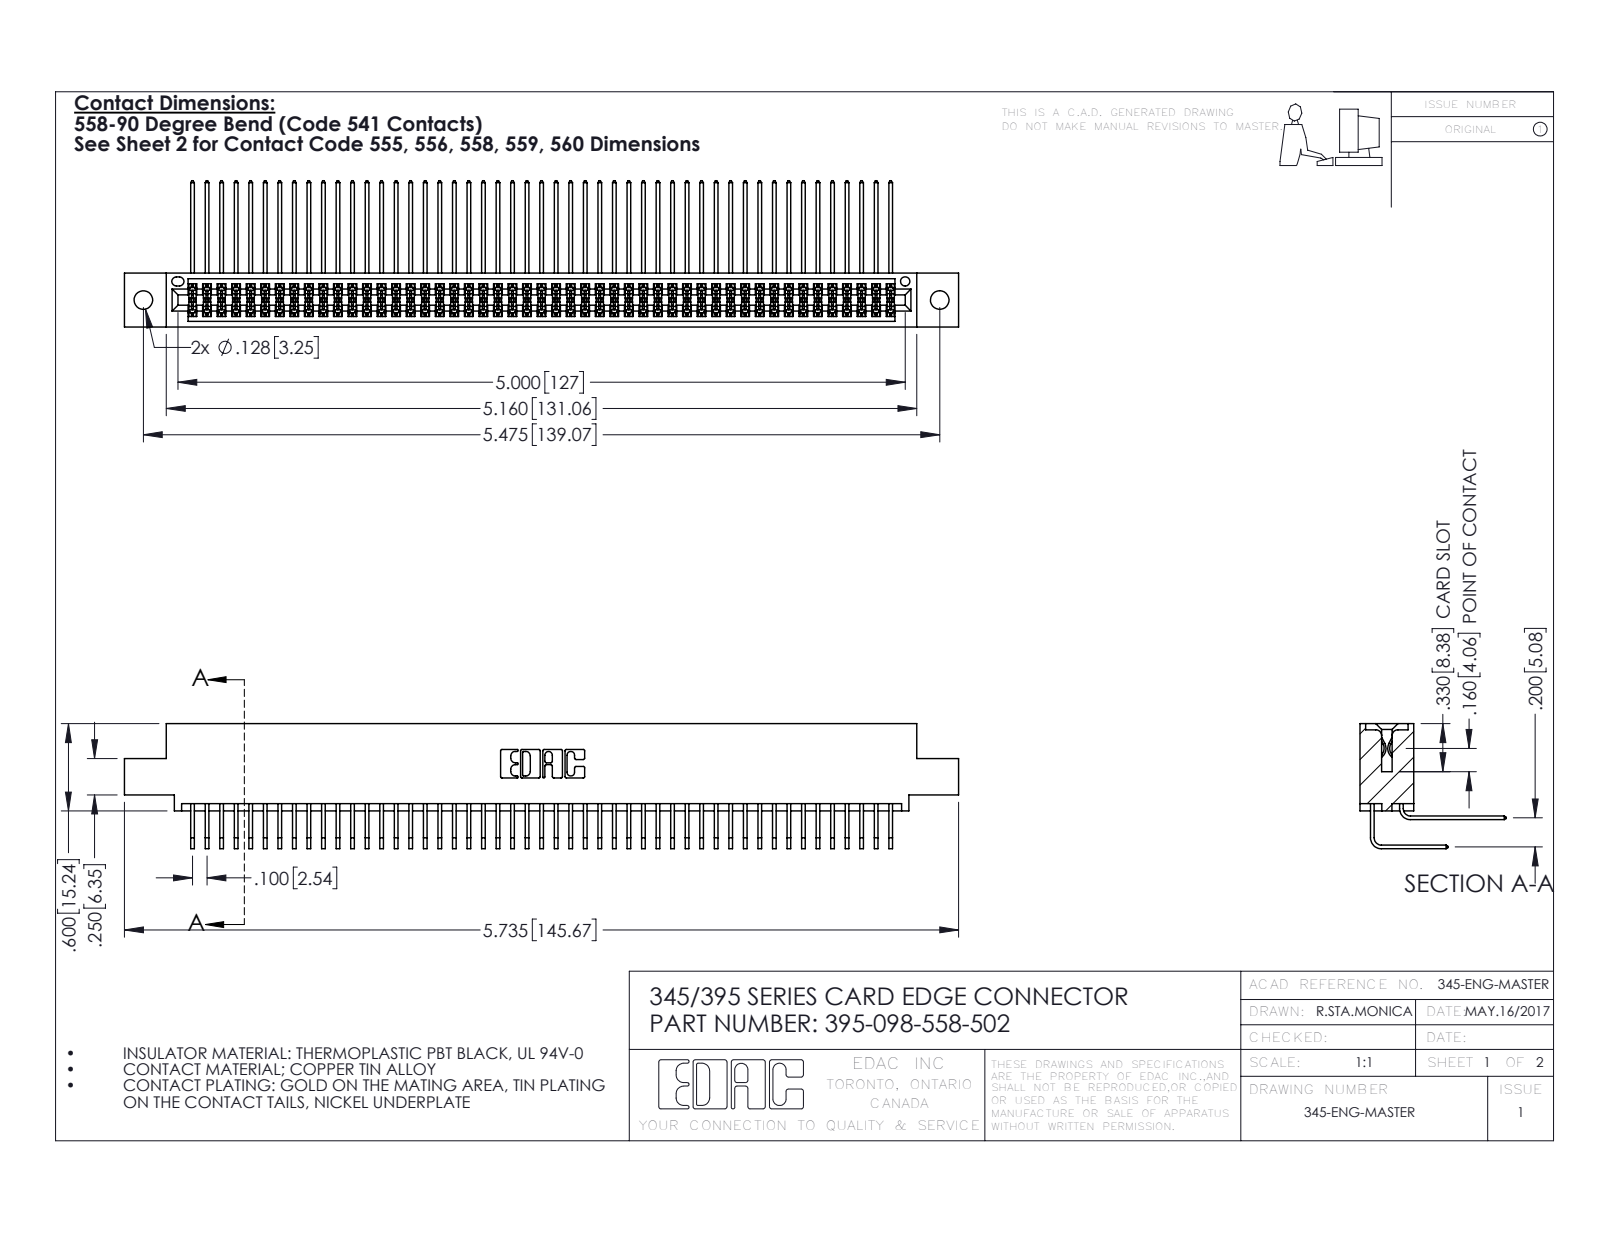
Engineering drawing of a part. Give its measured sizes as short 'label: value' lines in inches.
name: 345-292-001_558 559 Tail - 1; 345-292-001_558 Tail - 2; 395-098-558-502; 345 Part_0.110 Offset - 0.128 Dia
written by: SolidWorks 2016 (CONFIG_CONTROL_DESIGN)
unit: in
bodies: 99 solids, 5226 faces (3514 planar, 1712 cylindrical, 0 other)
size: 5.735 × 1.005 × 0.859
volume: 0.895 in³; area: 37.66 in²
holes: 2× ⌀0.128, 1× ⌀0.064
rounds: 148× R0.006, 22× R0.01, 6× R0.007, 6× R0.031, 3× R0.026, 2× R0.014, 2× R0.019, 2× R0.022
face distances: 0.072, 0.298, 0.2, 0.37, 0.098, 0.272, 0.025, 0.225, 0.025, 0.175
hole spacings: 0.27, 5.239, 5.475
